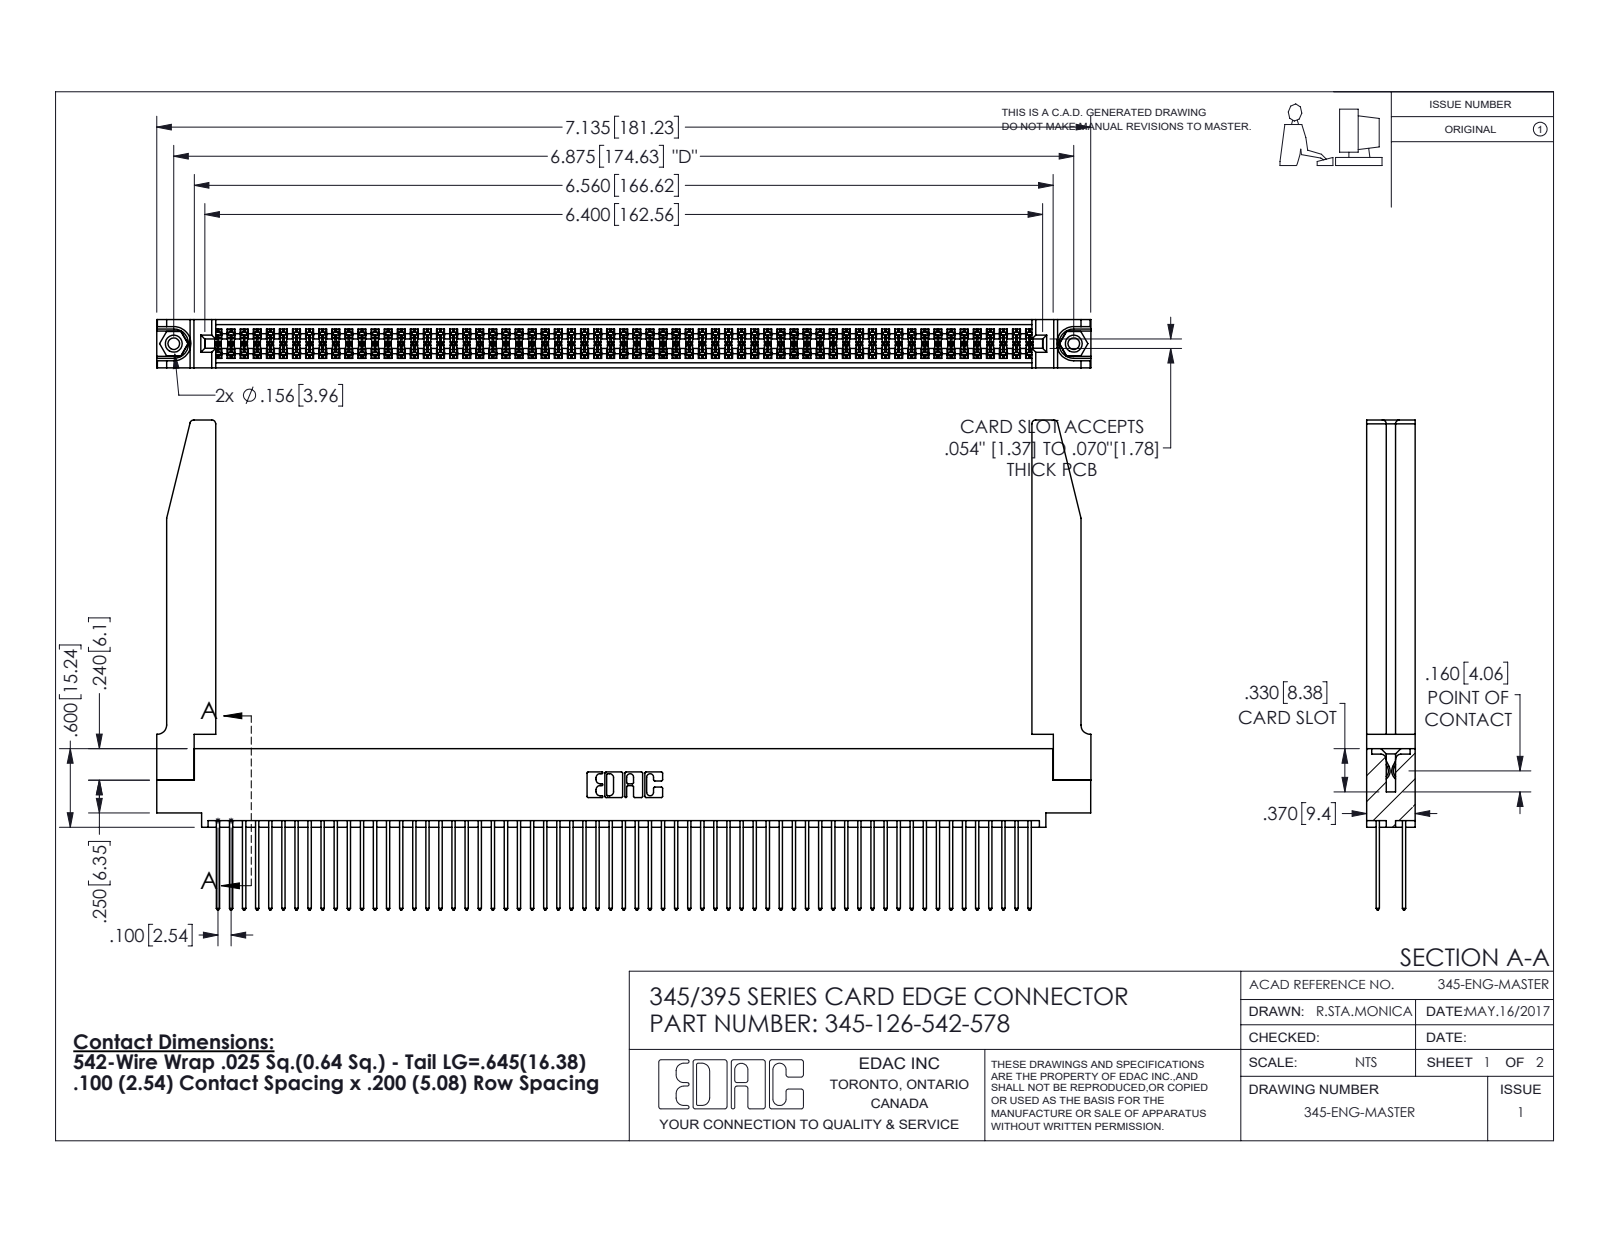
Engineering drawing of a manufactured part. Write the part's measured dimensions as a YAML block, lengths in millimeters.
part_name: "345-292-001_345-293-142; 345-126-542-578; 345-220-078_345-220-078; 345-250-001_345-250-001-102 (+1 more)"
step_written_by: "SolidWorks 2016 (CONFIG_CONTROL_DESIGN)"
units: millimeters
bodies: {solids: 131, faces: 6664, planar: 4384, cylindrical: 2228, other: 52}
overall_size: [181.3, 95, 9.4]
volume: 26090
surface_area: 37150
round_holes:
  - {diameter: 2.3, count: 2}
  - {diameter: 3.2, count: 2}
  - {diameter: 4, count: 2}
  - {diameter: 1.6, count: 1}
round_bosses_or_shafts:
  - {diameter: 3.9, count: 2}
partial_cylinders:
  - {radius: 0.2, count: 189}
  - {radius: 0.3, count: 126}
  - {radius: 0.3, count: 22}
  - {radius: 0.8, count: 8}
  - {radius: 0.2, count: 6}
  - {radius: 0.8, count: 6}
  - {radius: 0.7, count: 3}
  - {radius: 0.4, count: 2}
face_to_face_distances: [1.8, 7.6, 9.4, 5.1, 2.5, 6.9, 0.6, 5.7, 4.4, 3.8]
hole_center_spacings: [6.9, 168.6, 174.6]
